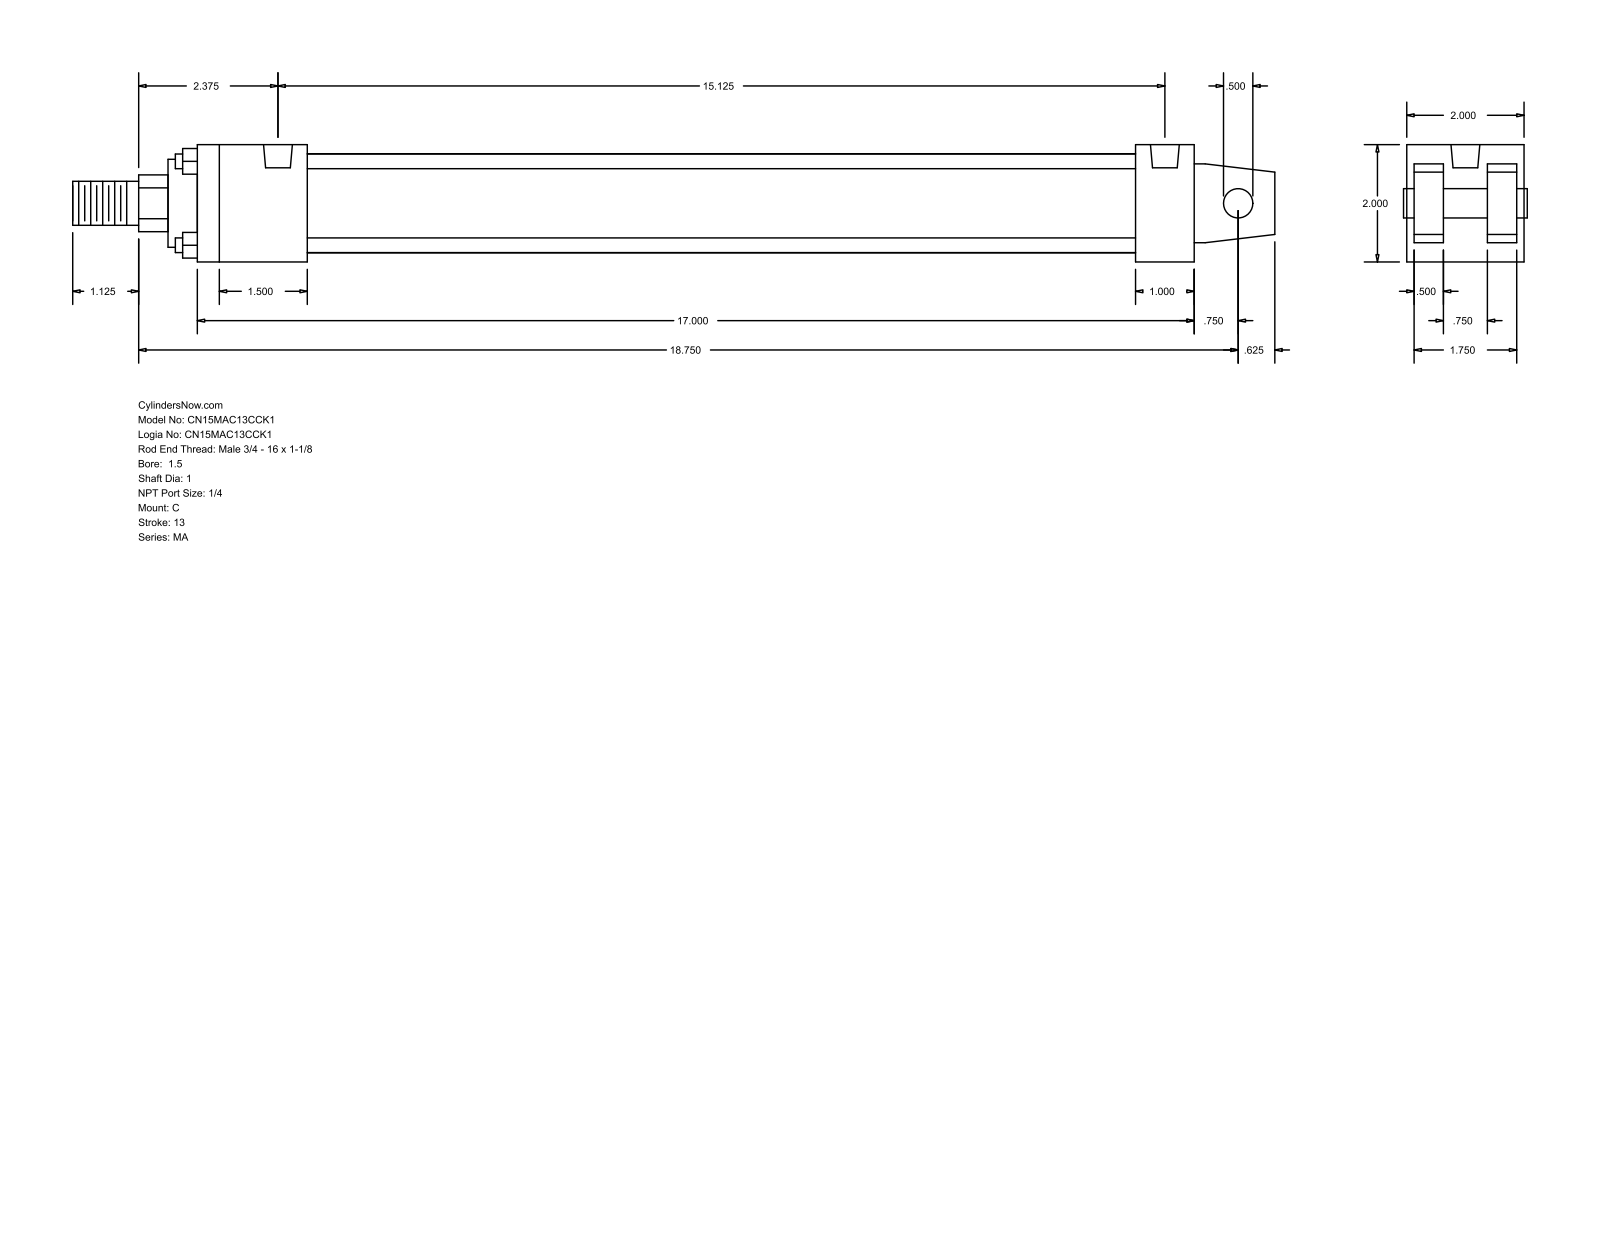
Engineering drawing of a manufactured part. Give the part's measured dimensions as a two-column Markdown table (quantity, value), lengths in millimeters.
| quantity | value |
| --- | --- |
| part name | MA_C__0150_1 |
| STEP written by | GSSL Pune (CONFIG_CONTROL_DESIGN) |
| units | millimeters |
| bodies | 0 solids, 103 faces (76 planar, 27 cylindrical, 0 other) |
| overall size | 520.7 × 50.8 × 50.8 |
| round holes (diameter × count) | 7.94 × 4, 12.49 × 2 |
| round bosses / shafts (diameter × count) | 6.35 × 4, 42.93 × 1, 38.1 × 1, 25.4 × 1, 19.05 × 1, 12.7 × 1 |
| partial cylindrical surfaces (radius × count) | 12.29 × 1 |
| main face-to-face distances | 50.8, 47.63, 12.7, 3.17, 15.87, 34.93, 31.76, 431.8, 25.4, 406.4 |
| hole center spacings | 384.17 |
